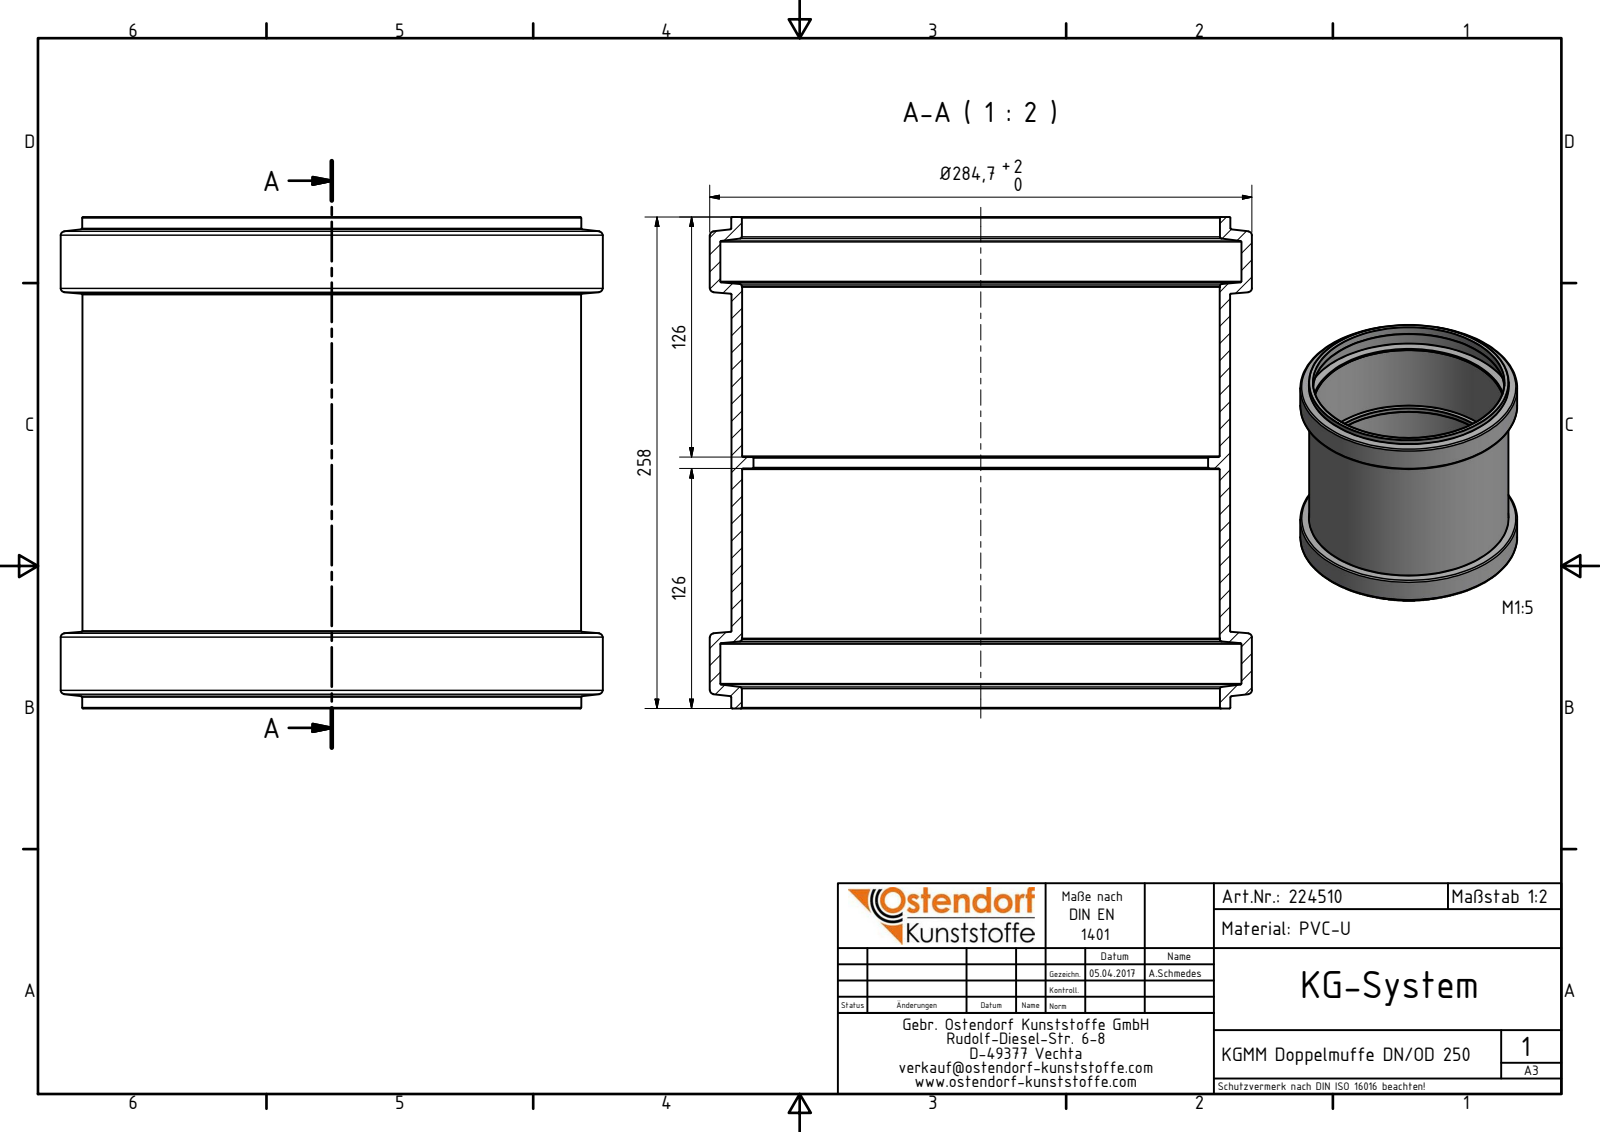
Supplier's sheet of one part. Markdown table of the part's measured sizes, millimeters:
| quantity | value |
| --- | --- |
| part name | 224510 KGMM Doppelmuffe DN_OD 250 |
| STEP written by | Autodesk Inventor 2016 (AUTOMOTIVE_DESIGN) |
| units | millimeters |
| bodies | 1 solid, 52 faces (6 planar, 14 cylindrical, 32 other) |
| overall size | 284.7 × 284.7 × 258 |
| volume | 1 379 000 mm³ |
| surface area | 504 414 mm² |
| round holes (diameter × count) | 238.8 × 1, 250.8 × 1, 251.1 × 1, 273.7 × 1 |
| round bosses / shafts (diameter × count) | 284.7 × 1, 262.1 × 1, 261.8 × 1 |
| main face-to-face distances | 126, 132, 6, 258, 36.68, 221.32, 89.32, 95.32, 184.64 |
